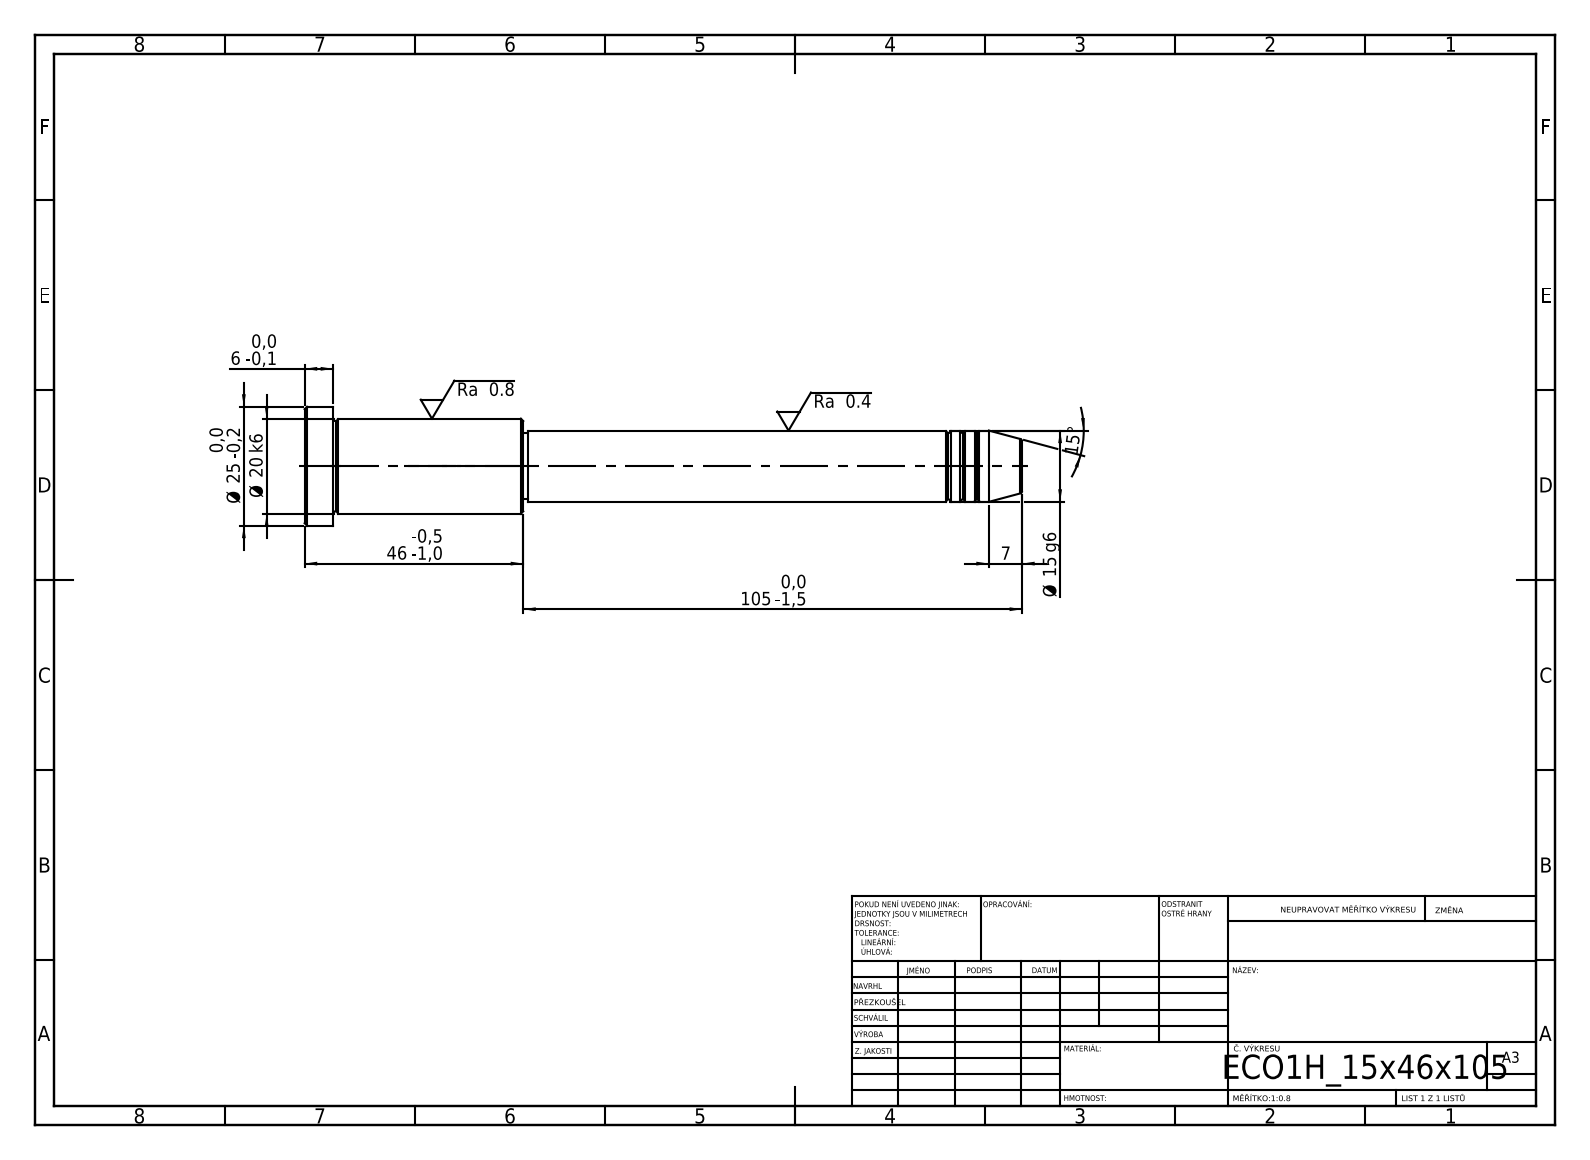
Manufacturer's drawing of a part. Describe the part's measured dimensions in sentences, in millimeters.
Its 3-D file was written by "SolidWorks 2019 (CONFIG_CONTROL_DESIGN)". It is 1 solid with 43 faces: 5 planar, 14 cylindrical and 24 other. Overall it measures 151 by 25 by 25 millimeters. Its volume is 33 664 cubic millimeters and its surface area 8 906 square millimeters. Round bosses or shafts: 1 of diameter 25, 1 of diameter 20, 1 of diameter 15, 1 of diameter 14. The main face-to-face distances are 6, 40, 46, 105, 145, 151, 104, 1, 41, 47.
